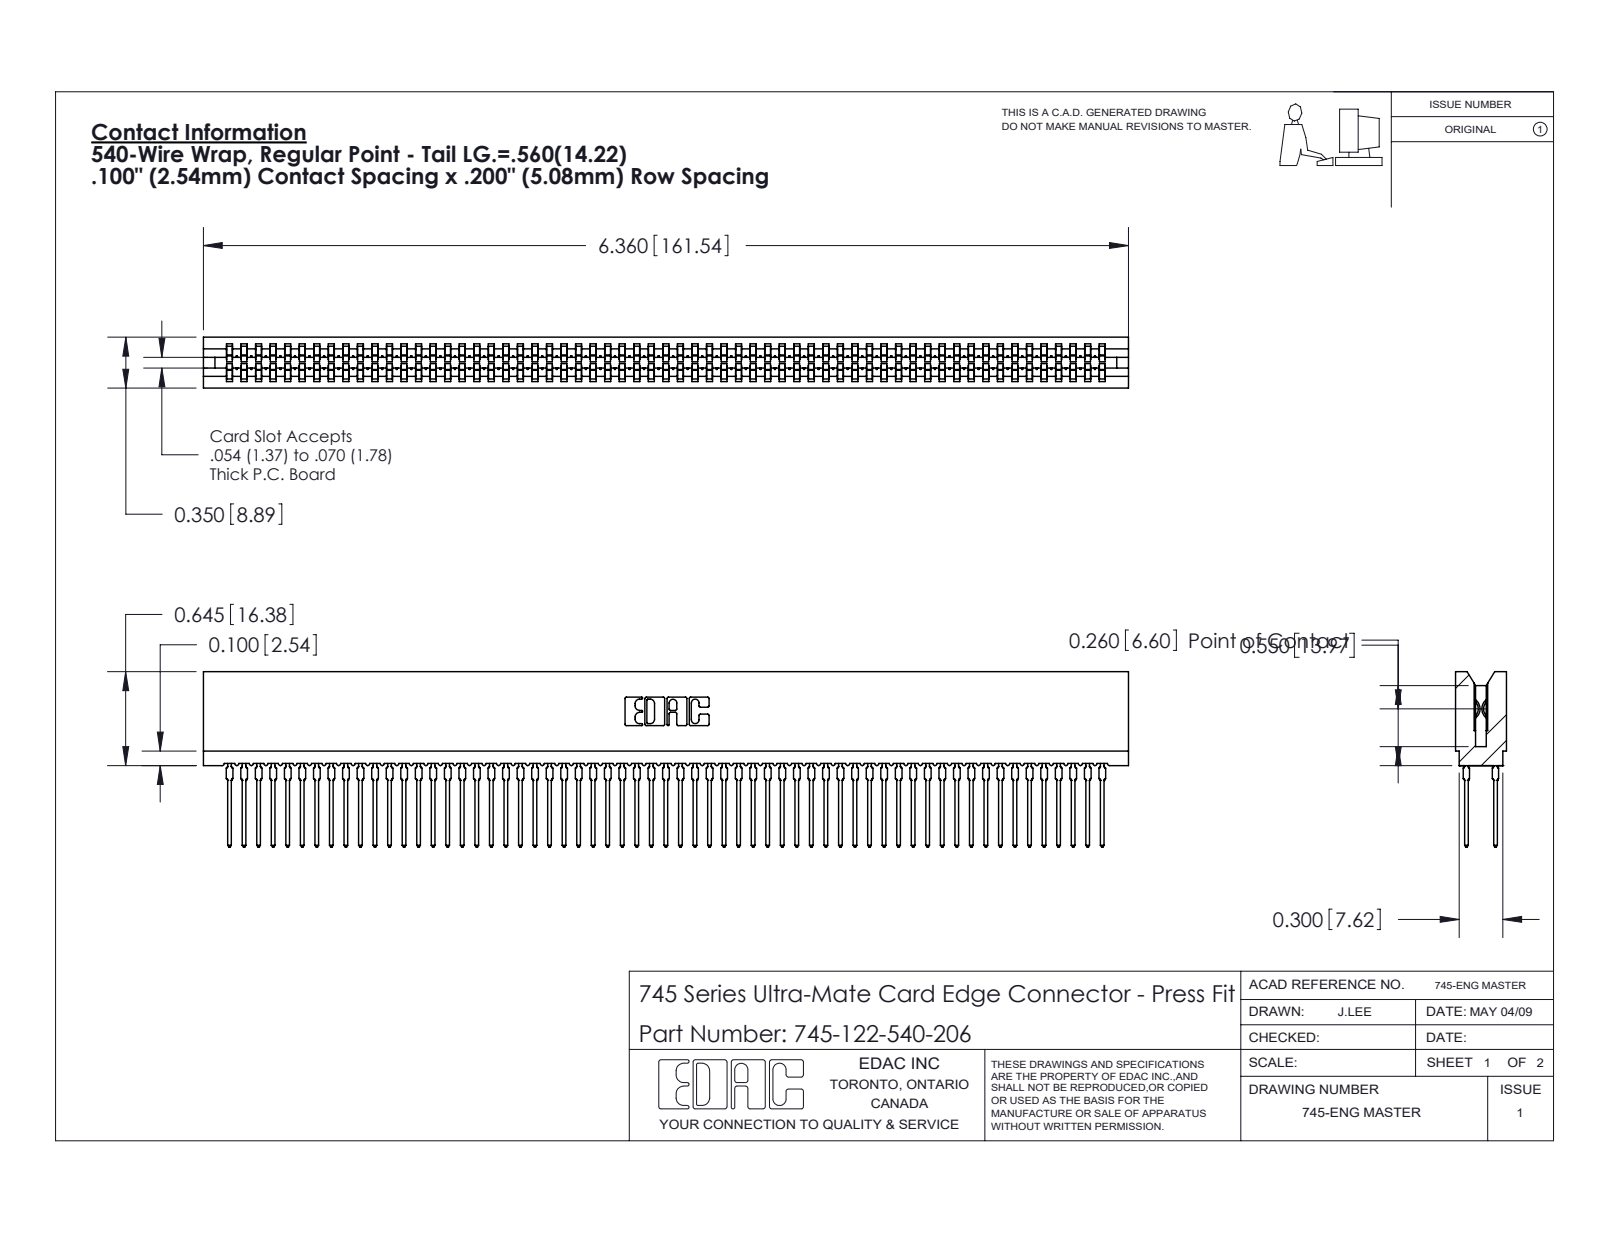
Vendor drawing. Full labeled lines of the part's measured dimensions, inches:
Part name (STEP PRODUCT): 745-292-001_540; 745 Part_Insulator Option - 06; 745-122-540-206
STEP written by: SolidWorks 2020 (CONFIG_CONTROL_DESIGN)
Units: inches
Bodies: 123 solids, 11015 faces (5668 planar, 2175 cylindrical, 3172 other)
Overall size (bounding box): 6.36 × 1.206 × 0.35
Volume: 0.901 in³ · Surface area: 49.45 in²
Partial cylindrical surfaces — rounded edges, fillets, slot ends (radius × count): R0.021 ×244, R0.015 ×122, R0.01 ×22, R0.005 ×8, R0.011 ×8, R0.007 ×6, R0.031 ×6, R0.026 ×3
Main face-to-face distances: 0.063, 0.287, 0.35, 0.2, 0.045, 0.305, 0.018, 0.243, 0.138, 0.212
